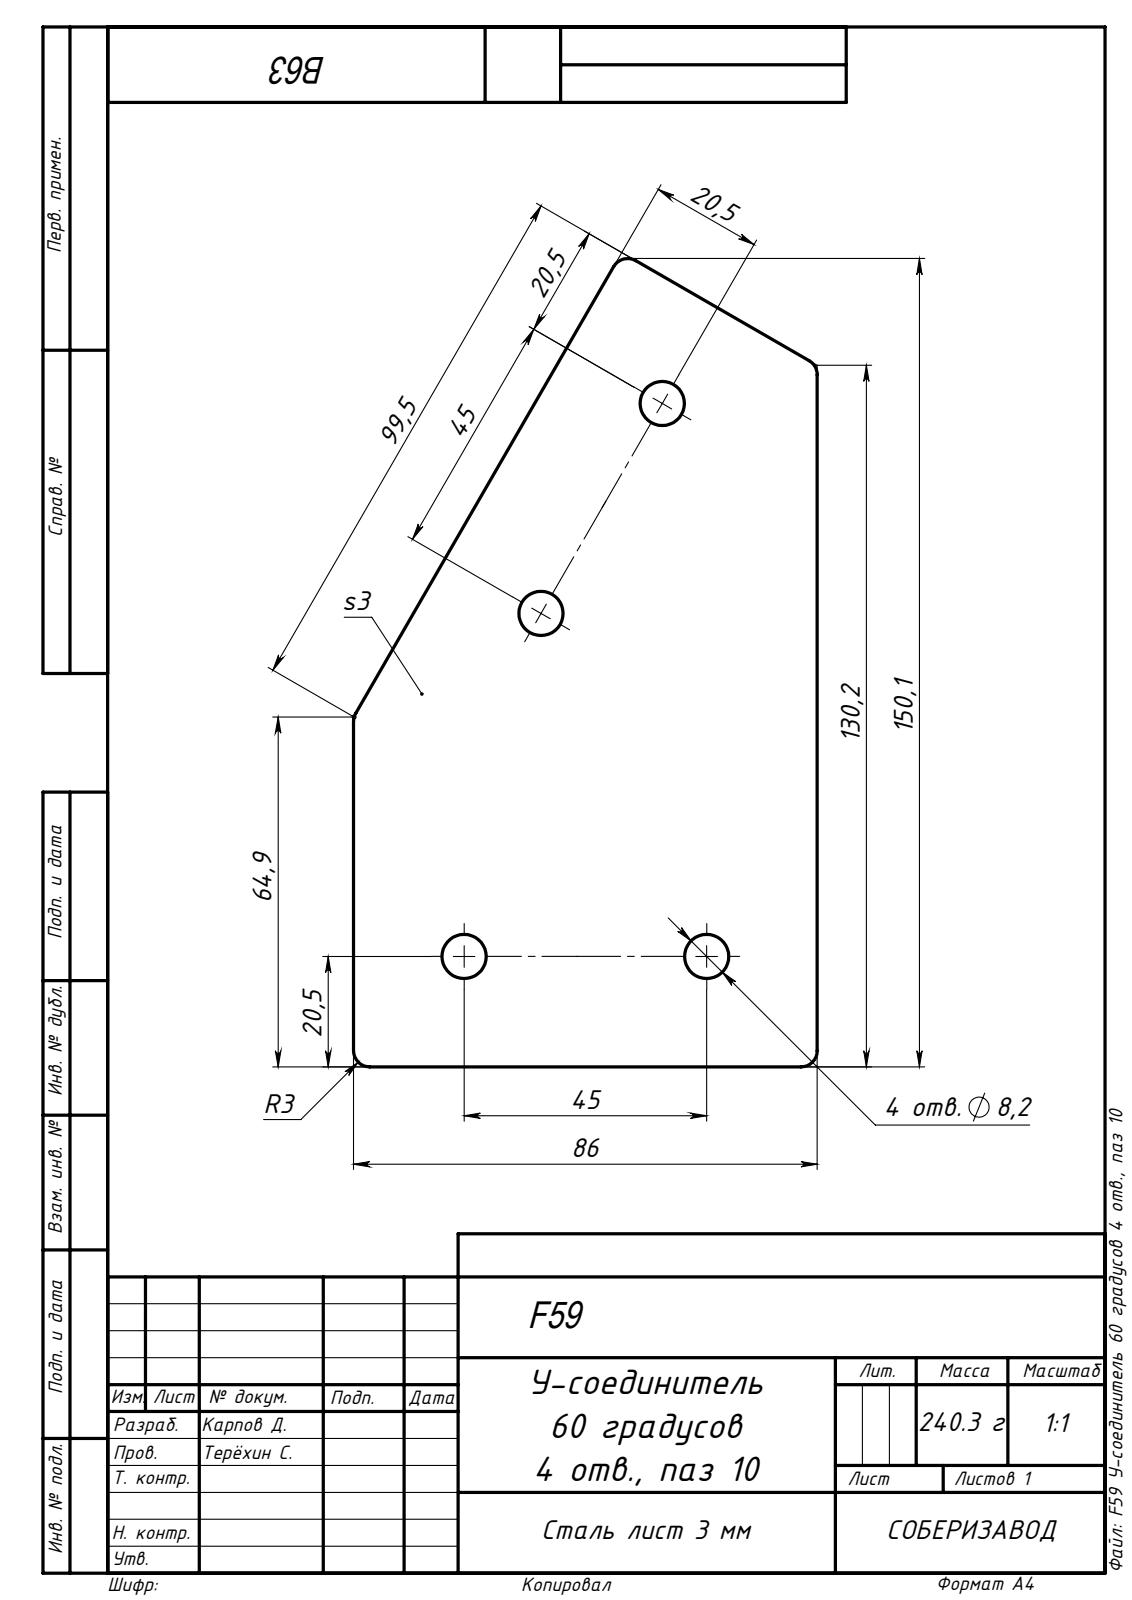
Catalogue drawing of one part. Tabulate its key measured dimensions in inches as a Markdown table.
| quantity | value |
| --- | --- |
| part name | F59 У-соединитель 60 градусов 4 отв., паз 10 |
| STEP written by | SolidWorks 2020 (AUTOMOTIVE_DESIGN) |
| units | inches |
| bodies | 1 solid, 20 faces (7 planar, 13 cylindrical, 0 other) |
| overall size | 5.907 × 3.386 × 0.118 |
| volume | 1.878 in³ |
| surface area | 34.22 in² |
| round holes (diameter × count) | 0.323 × 4 |
| partial cylindrical surfaces (radius × count) | 0.118 × 5 |
| main face-to-face distances | 0.118, 3.386 |
| hole center spacings | 1.772, 2.569, 2.784, 4.054, 4.293 |
